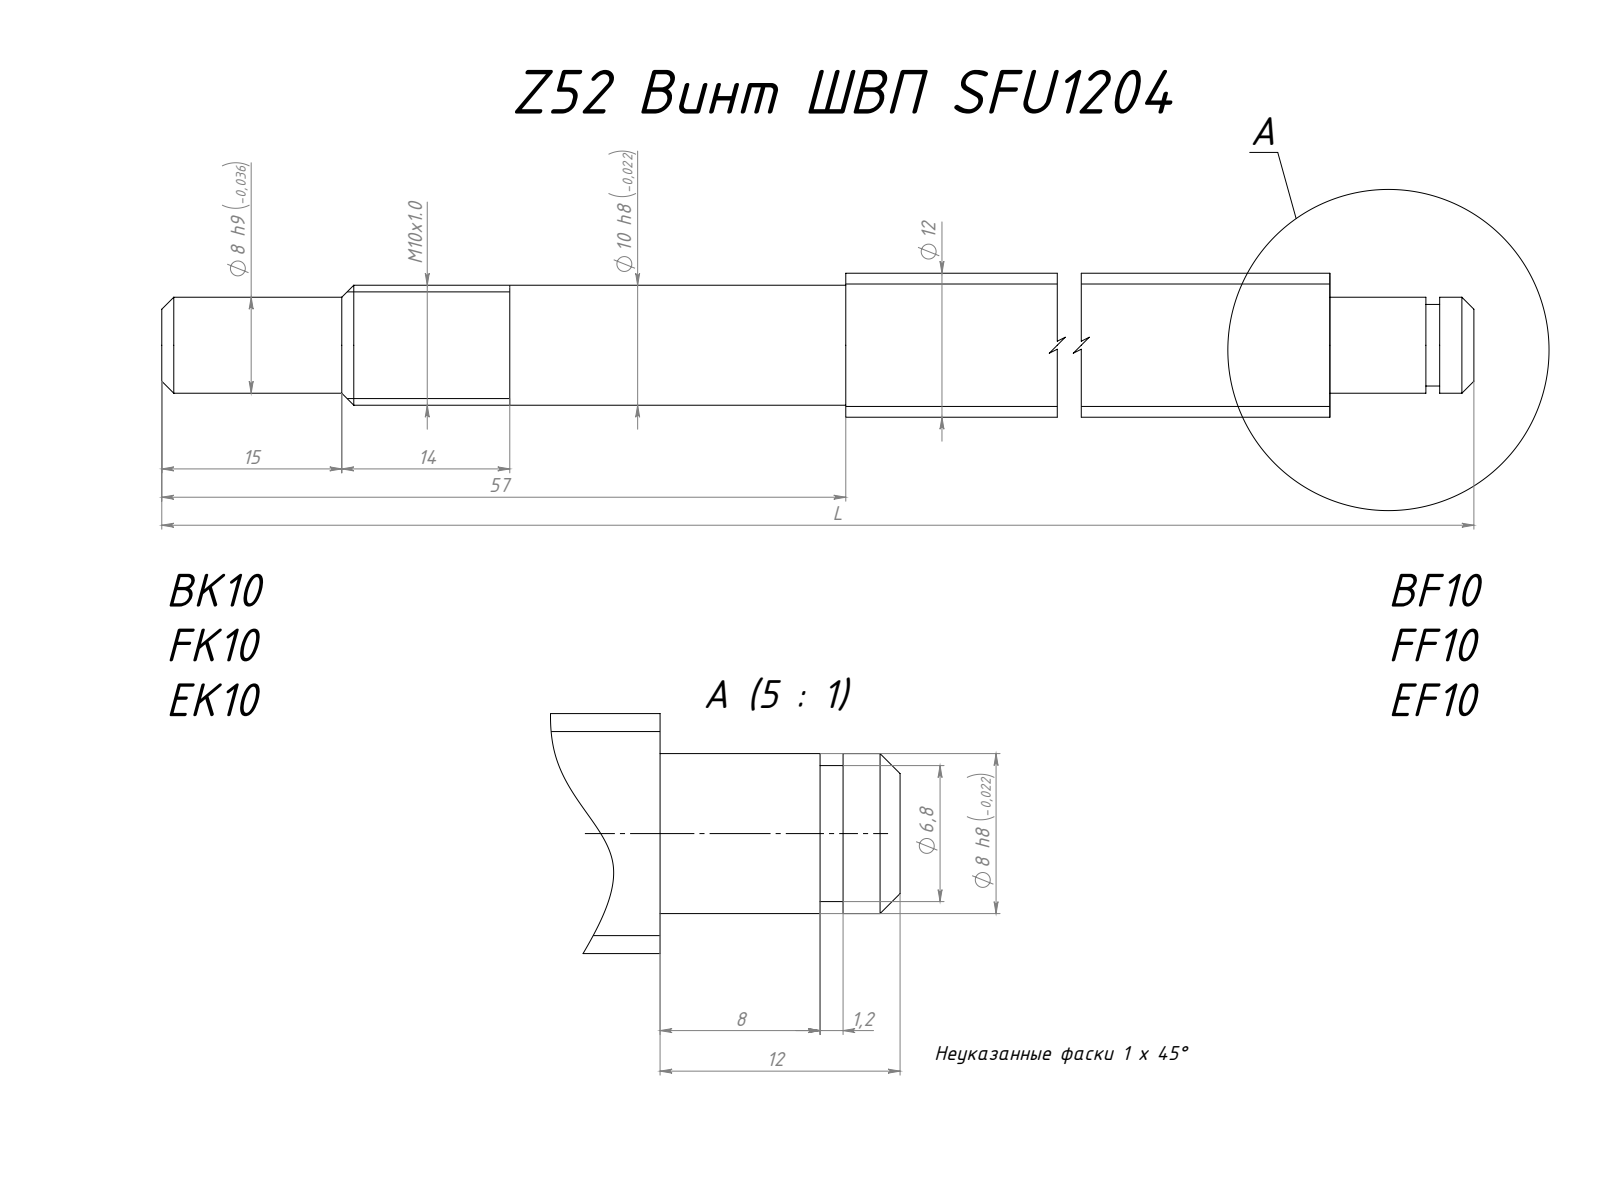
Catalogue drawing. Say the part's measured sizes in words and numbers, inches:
The part is named "Z52 Винт ШВП SFU1204 - токарная обработка BK-BF, FK-FF, EK-EF-10". Its 3-D file was written by "SolidWorks 2026 (AUTOMOTIVE_DESIGN)". It is 1 solid with 24 faces: 6 planar, 12 cylindrical and 6 other. Overall it measures 118.11 by 0.472 by 0.472 inches. Its volume is 20.51 cubic inches and its surface area 174.7 square inches. Round bosses or shafts: 1 of diameter 0.472, 1 of diameter 0.394, 1 of diameter 0.315, 1 of diameter 0.268. The main face-to-face distances are 115.394, 2.244, 117.638, 118.11, 115.866, 0.472, 117.953, 115.709, 0.315, 0.157.
